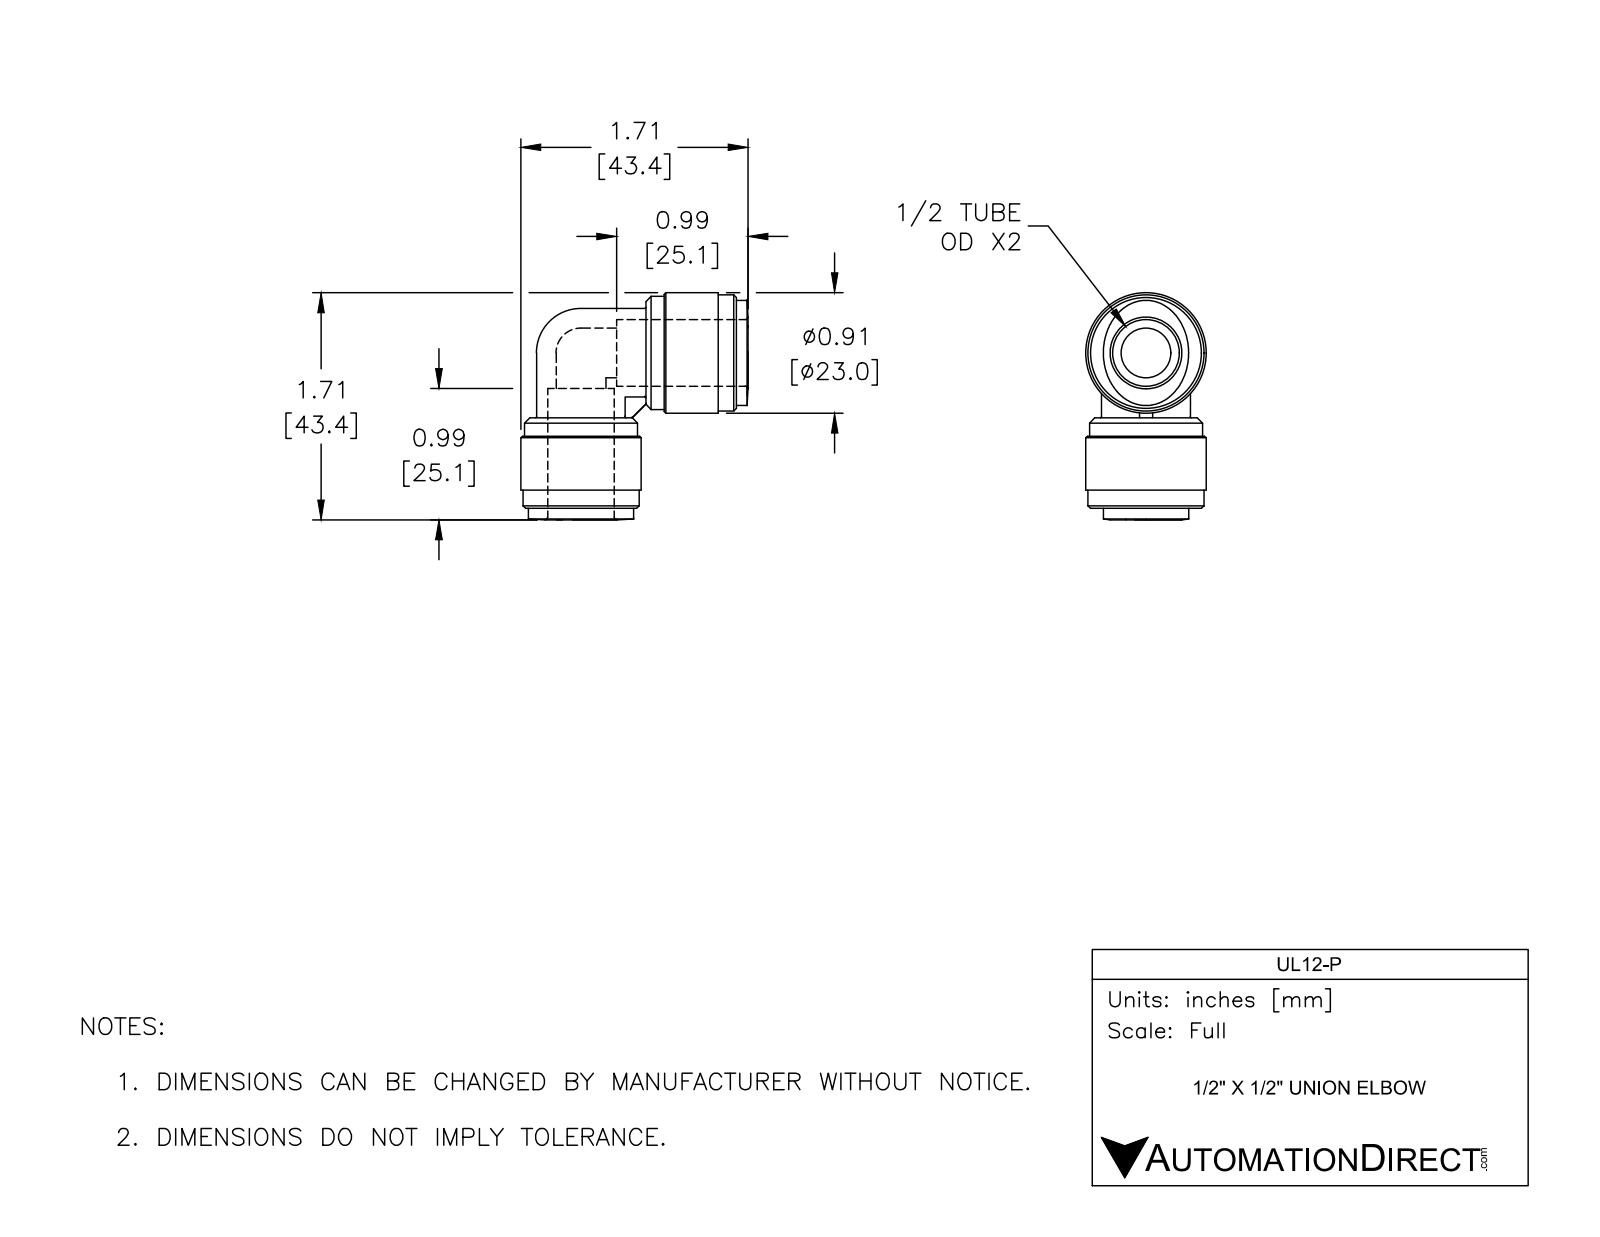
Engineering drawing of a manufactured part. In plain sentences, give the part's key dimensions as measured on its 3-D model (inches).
The part is named "UL12-P". Its 3-D file was written by "SolidWorks 2017 (AUTOMOTIVE_DESIGN)". It is 1 solid with 70 faces: 12 planar, 25 cylindrical and 33 other. Overall it measures 1.709 by 1.709 by 0.906 inches. Its volume is 0.796 cubic inches and its surface area 11.22 square inches. Round holes: 2 of diameter 0.374, 2 of diameter 0.5. Round bosses or shafts: 2 of diameter 0.906, 2 of diameter 0.874, 2 of diameter 0.85, 2 of diameter 0.669. The main face-to-face distances are 0.681, 0.138, 0.543, 0.902, 0.22, 0.764, 0.406, 0.358, 0.098.
